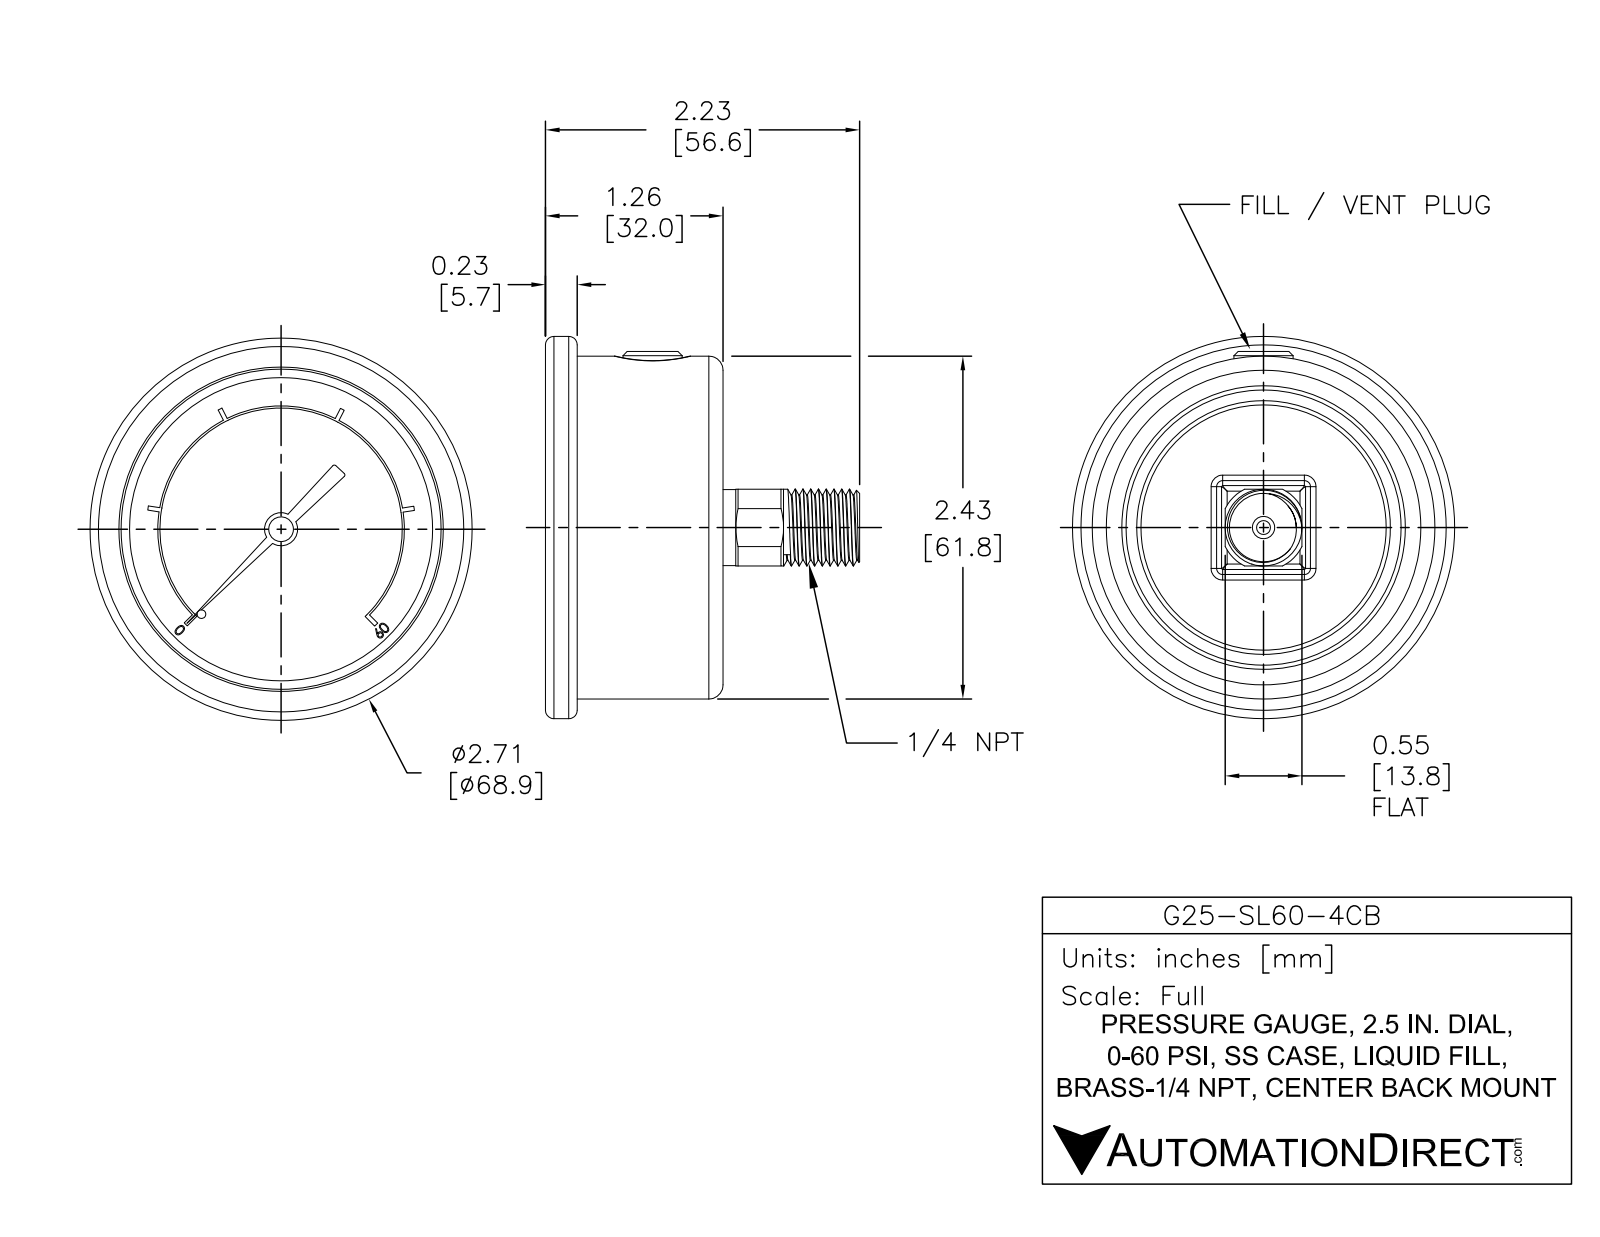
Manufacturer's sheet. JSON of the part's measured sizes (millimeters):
{"part_name": "G25-SL60-4CB", "step_written_by": "SolidWorks 2021 (AUTOMOTIVE_DESIGN)", "units": "millimeters", "bodies": {"solids": 1, "faces": 344, "planar": 204, "cylindrical": 83, "other": 57}, "overall_size": [68.9, 68.9, 56.6], "volume_mm3": 84690, "surface_area_mm2": 16010, "round_holes": [[1.8, 1], [2.5, 1], [57.7, 1]], "round_bosses_or_shafts": [[68.9, 1], [61.8, 1], [13.8, 1], [13.7, 1], [10.7, 1], [6, 1], [4.5, 1], [3.6, 1]], "partial_cylinders_radius": [[1.5, 8], [0.4, 2], [7.7, 1], [21.8, 1], [22.2, 1]], "face_to_face_distances": [24.1, 30.5, 6.4, 1.5, 25.7, 32, 26.3, 24.8, 0.6, 5.7]}
